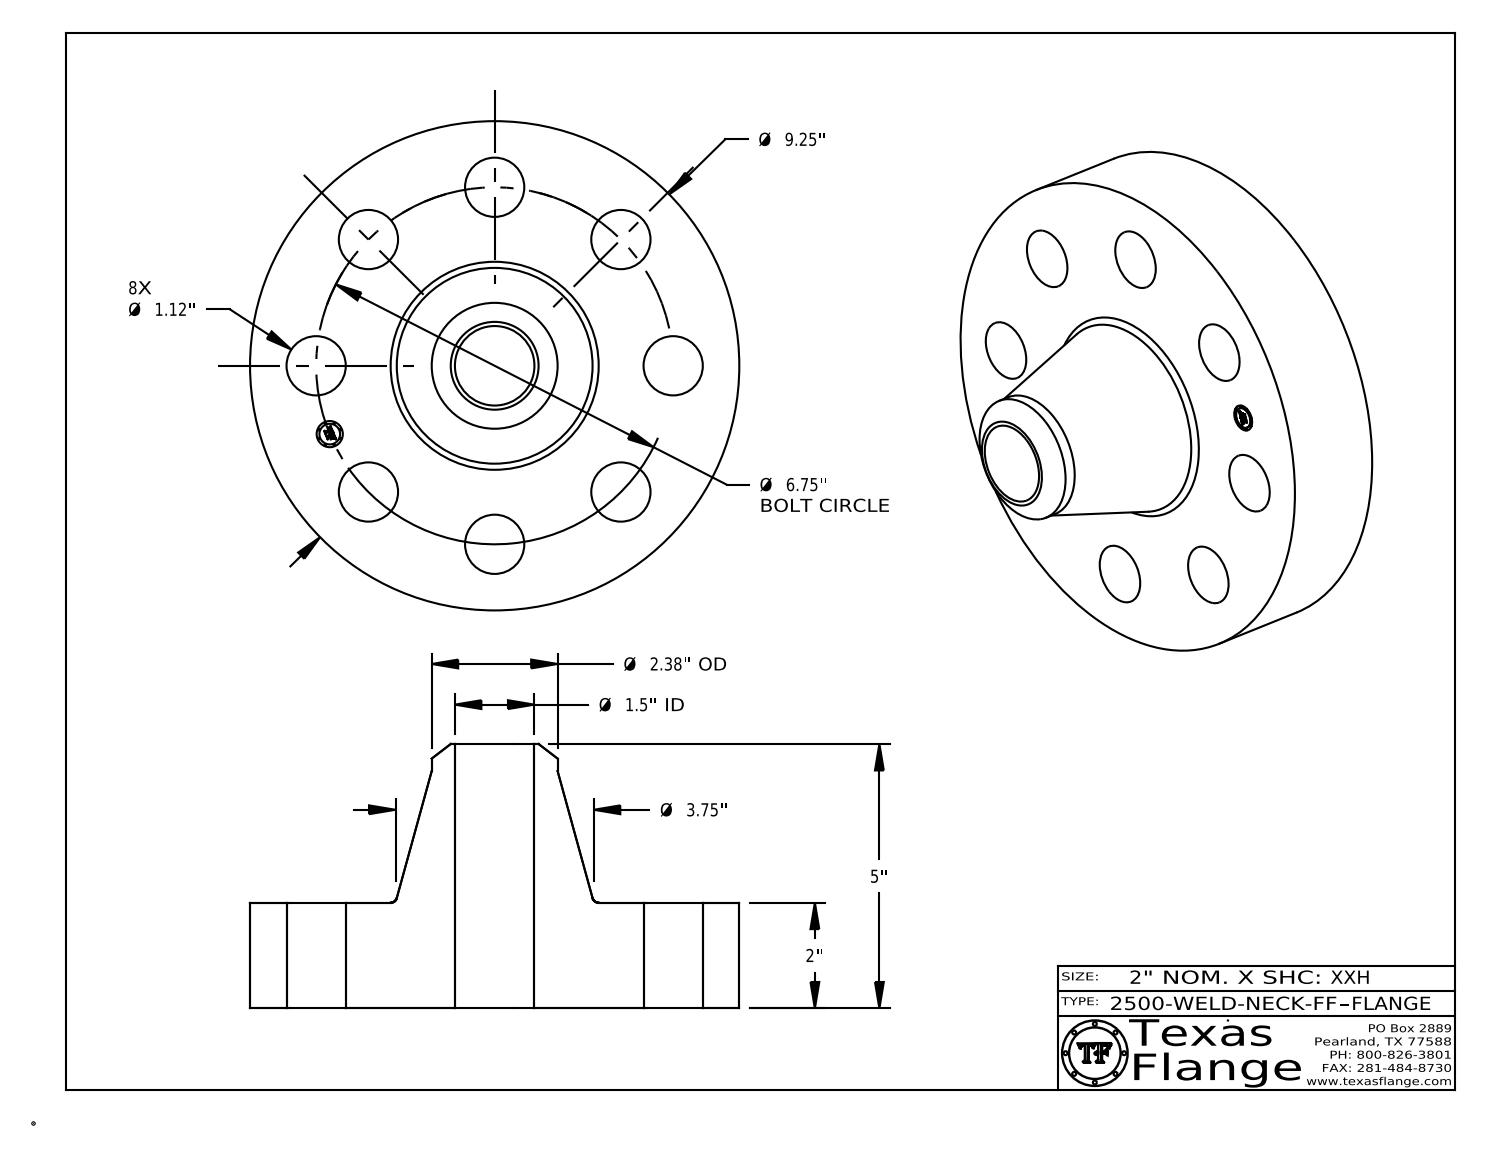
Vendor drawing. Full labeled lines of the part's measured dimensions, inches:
Part name (STEP PRODUCT): 2500-WELD-NECK-FF
STEP written by: CATIA V5 STEP AP214 (AUTOMOTIVE_DESIGN)
Units: inches
Bodies: 1 solid, 416 faces (368 planar, 42 cylindrical, 6 other)
Overall size (bounding box): 9.25 × 9.25 × 5
Volume: 130.4 in³ · Surface area: 273.5 in²
Round holes (diameter × count): ⌀1.12 ×8, ⌀0.495 ×1, ⌀1.503 ×1
Round bosses / shafts (diameter × count): ⌀0.03 ×8, ⌀9.25 ×1, ⌀2.38 ×1, ⌀0.39 ×1
Main face-to-face distances: 2, 5, 3, 1.985, 0.015, 3.015, 0.148, 0.145, 0.027, 0.096
Hole centre spacings: 3.375, 2.583, 4.773, 6.237, 6.75, 1.317, 5.613, 6.62
